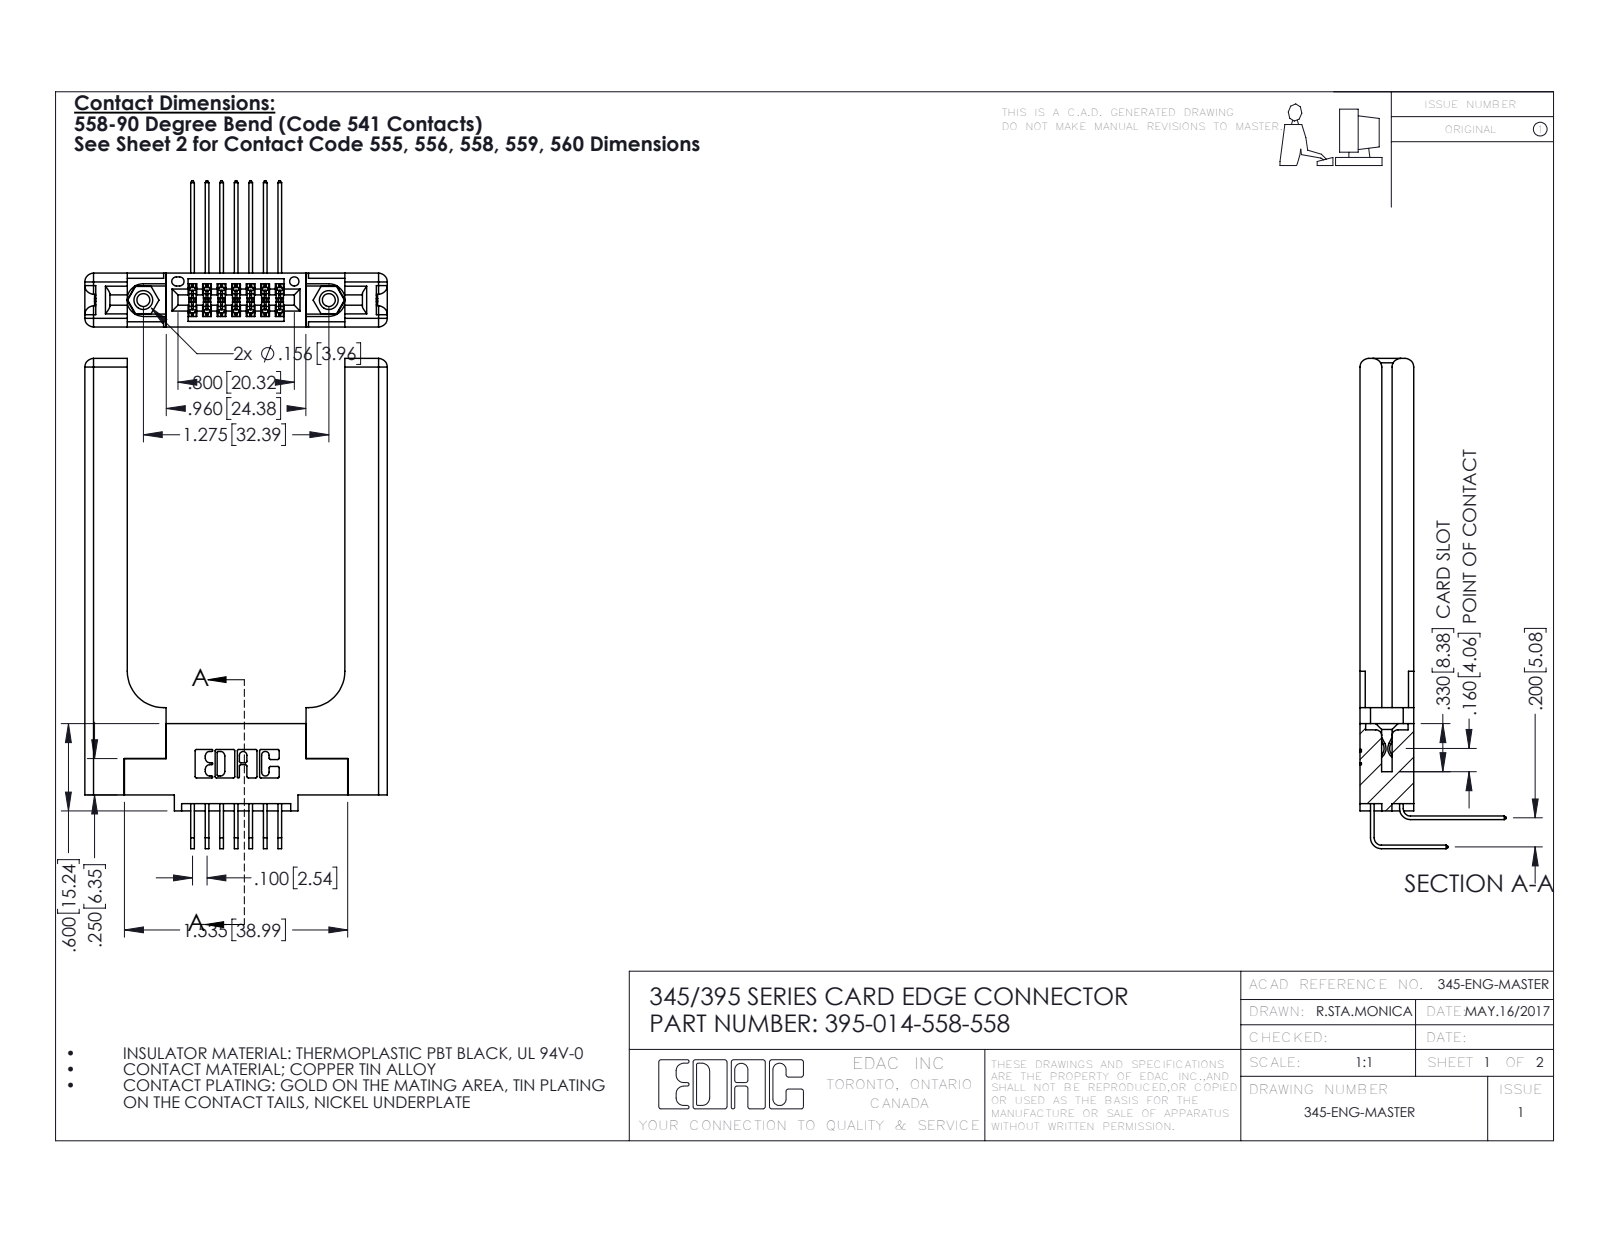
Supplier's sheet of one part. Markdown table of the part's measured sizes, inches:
| quantity | value |
| --- | --- |
| part name | 345-292-001_558 559 Tail - 1; 395-014-558-558; 345-220-058_345-220-058; 345-250-001_345-250-001-102 (+2 more) |
| STEP written by | SolidWorks 2016 (CONFIG_CONTROL_DESIGN) |
| units | inches |
| bodies | 19 solids, 1114 faces (722 planar, 332 cylindrical, 60 other) |
| overall size | 3.369 × 2.079 × 1.005 |
| volume | 0.811 in³ |
| surface area | 18.55 in² |
| round holes (diameter × count) | 0.089 × 2, 0.125 × 2, 0.156 × 2, 0.064 × 1 |
| round bosses / shafts (diameter × count) | 0.155 × 2 |
| partial cylindrical surfaces (radius × count) | 0.006 × 22, 0.01 × 22, 0.06 × 16, 0.007 × 6, 0.031 × 6, 0.026 × 3, 0.014 × 2, 0.019 × 2 |
| main face-to-face distances | 0.37, 0.15, 0.22, 0.072, 0.148, 0.077, 0.298, 1.496, 0.2, 0.071 |
| hole center spacings | 0.27, 1.045, 1.275 |
